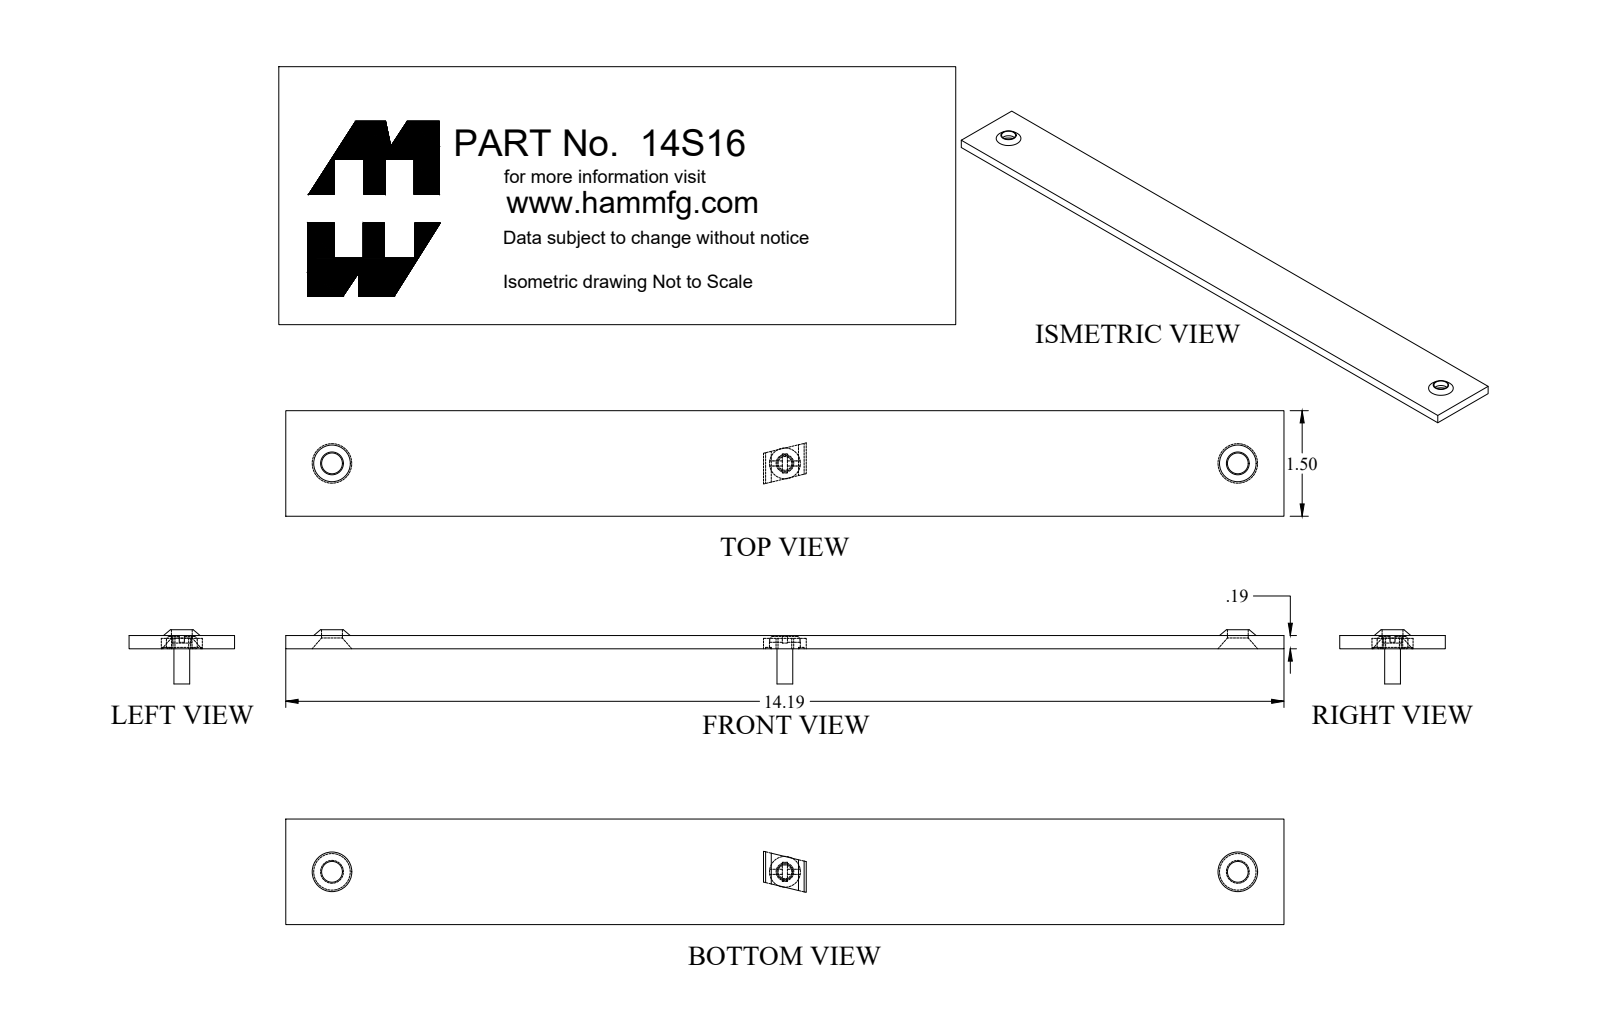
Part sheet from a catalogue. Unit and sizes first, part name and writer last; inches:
Units: inches
Overall size (bounding box): 14.187 × 1.5 × 0.27
Round holes (diameter × count): ⌀0.296 ×2
Main face-to-face distances: 0.188, 1.5, 14.187, 0.27, 0.082
Hole centre spacings: 12.875
Volume: 3.962 in³ · Surface area: 48.67 in²
Bodies: 1 solid, 14 faces (8 planar, 2 cylindrical, 4 other)
Part name (STEP PRODUCT): 14S16
STEP written by: SolidWorks 2018 (AUTOMOTIVE_DESIGN)
